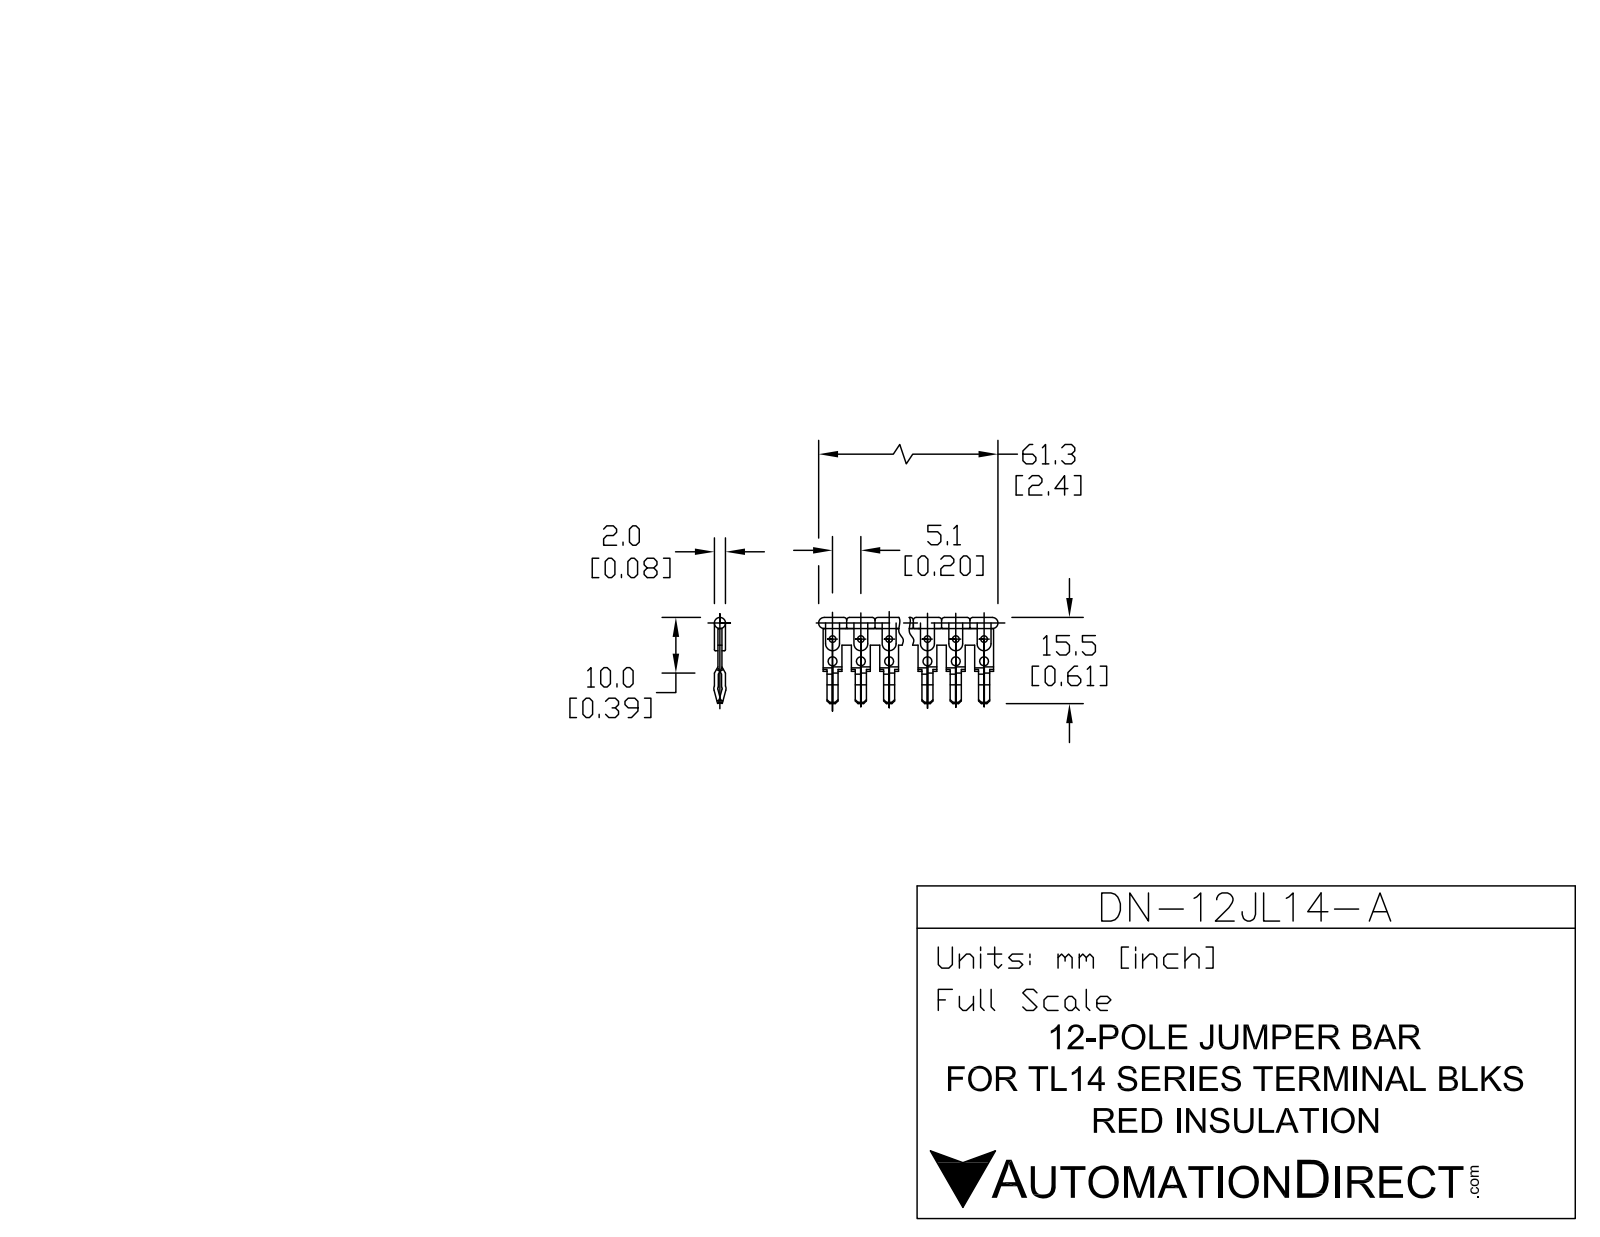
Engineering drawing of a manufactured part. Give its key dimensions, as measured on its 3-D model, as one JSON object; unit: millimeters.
{"part_name": "43531_12_RDS_DN-12JL14-A", "step_written_by": "SolidWorks 2013 (AUTOMOTIVE_DESIGN)", "units": "millimeters", "bodies": {"solids": 2, "faces": 847, "planar": 419, "cylindrical": 332, "other": 96}, "overall_size": [61.1, 15.5, 2.08], "volume_mm3": 756, "surface_area_mm2": 2220, "round_holes": [[1.2, 12], [1.3, 12]], "round_bosses_or_shafts": [[2, 1]], "partial_cylinders_radius": [[0.25, 48], [1.25, 12], [0.48, 4], [0.7, 4], [0.5, 3]], "face_to_face_distances": [0.7, 0.65, 1.35, 0.55, 2, 1.9, 1.25, 0.8, 1.2, 1.1], "hole_center_spacings": [5.1, 6.48, 10.2, 10.96, 15.3, 15.81, 20.4, 20.79]}
